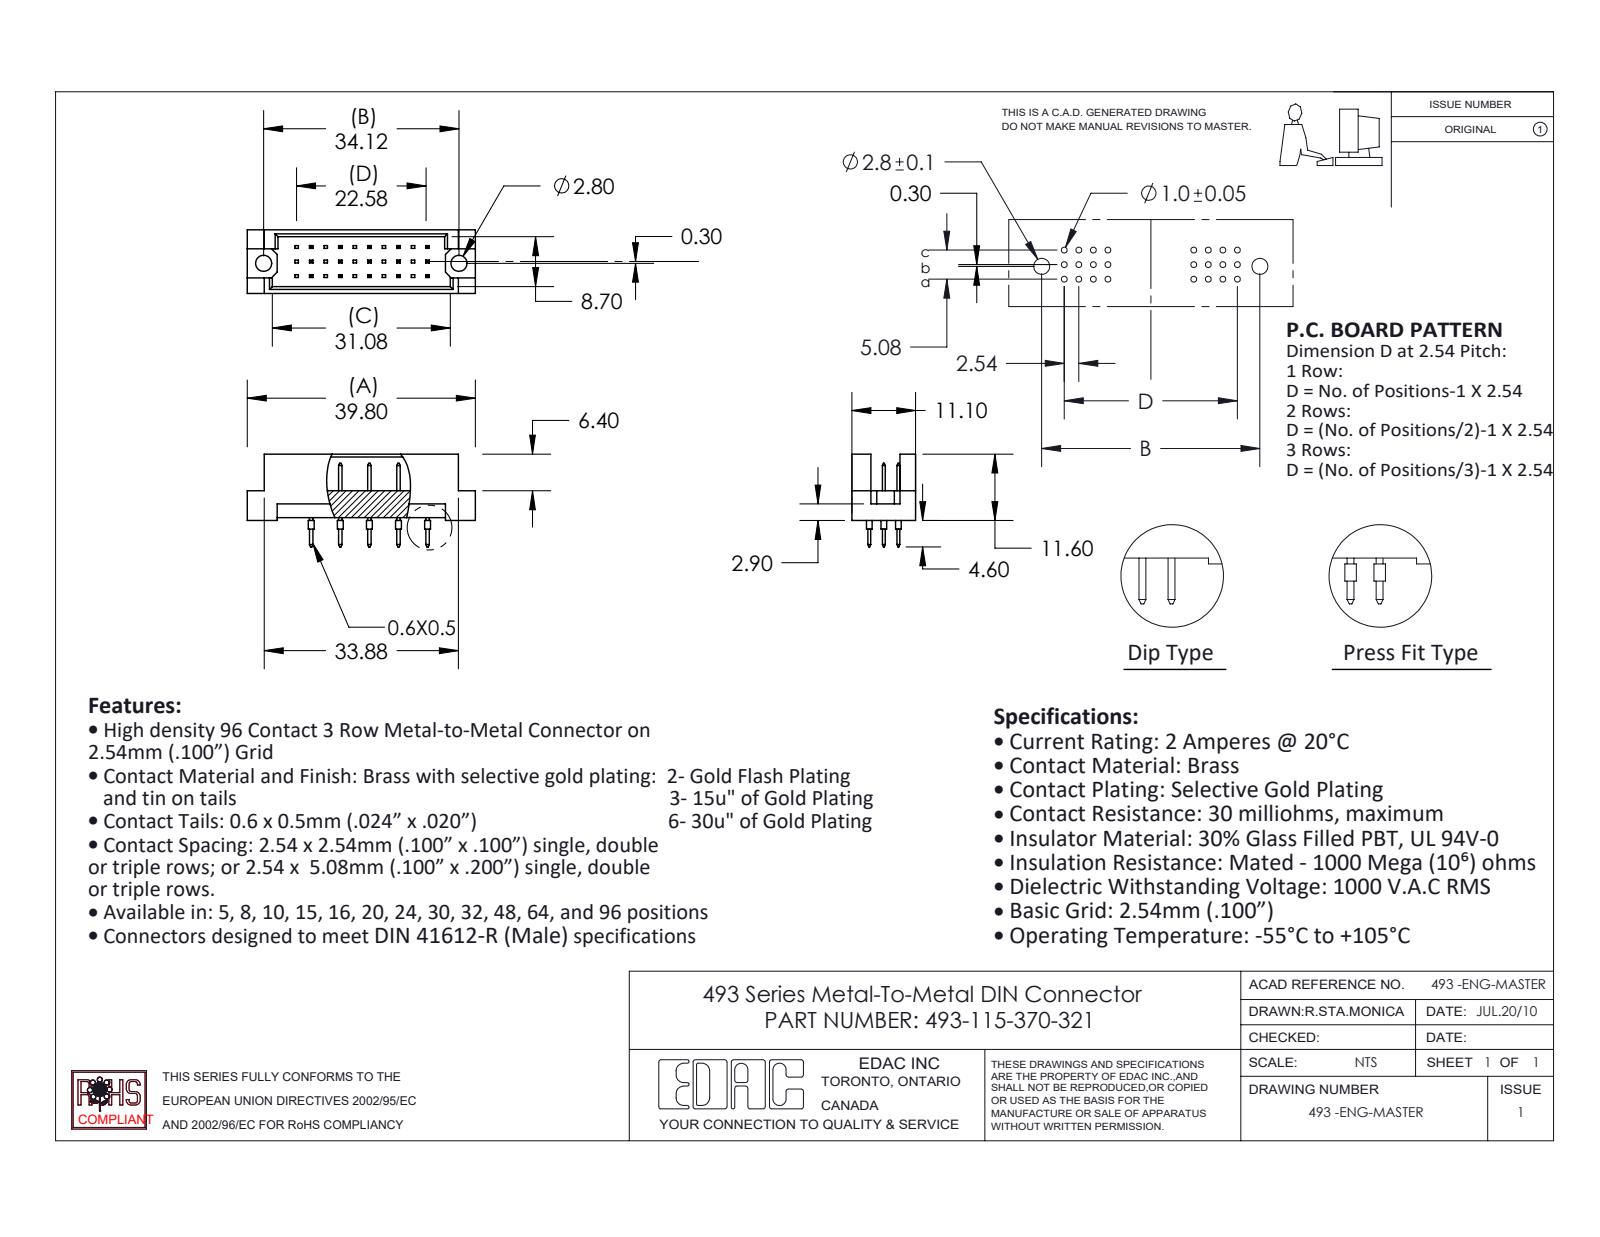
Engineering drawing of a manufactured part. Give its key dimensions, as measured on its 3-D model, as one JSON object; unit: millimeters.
{"part_name": "493 Part_30; 493-290_70; 493-115-370-322", "step_written_by": "SolidWorks 2020 (CONFIG_CONTROL_DESIGN)", "units": "millimeters", "bodies": {"solids": 16, "faces": 502, "planar": 468, "cylindrical": 34, "other": 0}, "overall_size": [39.8, 16.2, 11.1], "volume_mm3": 2448, "surface_area_mm2": 3250, "round_holes": [[2.8, 2]], "round_bosses_or_shafts": [[1, 15]], "face_to_face_distances": [1.2, 9.9, 11.1, 5.08, 0.5, 8.7, 2.54, 4.7, 10.16, 2.4], "hole_center_spacings": [34.12]}
